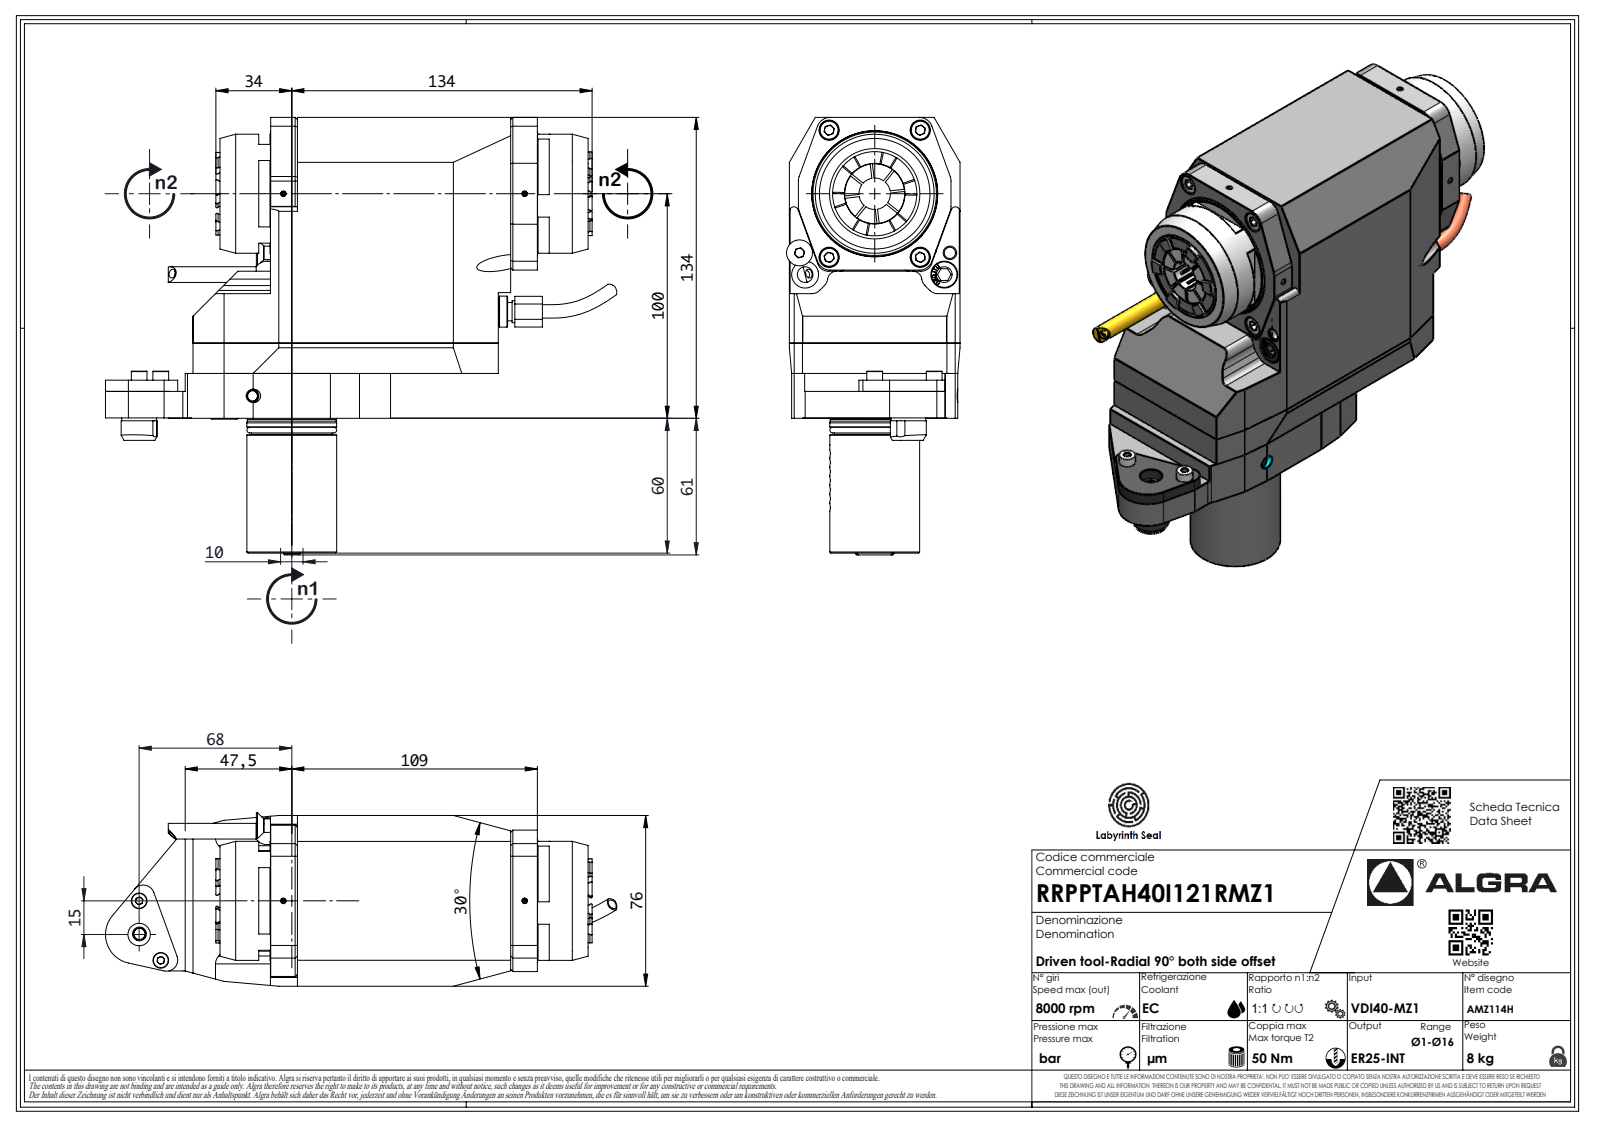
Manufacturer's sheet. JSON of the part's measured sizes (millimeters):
{"part_name": "RRPPTAH40I121RMZ1", "step_written_by": "SolidWorks 2023 (AUTOMOTIVE_DESIGN)", "units": "millimeters", "bodies": {"solids": 1, "faces": 599, "planar": 436, "cylindrical": 87, "other": 76}, "overall_size": [227.81, 194.8, 76], "volume_mm3": 1331000, "surface_area_mm2": 94605, "round_holes": [[5, 2], [2.1, 1], [4, 1], [6, 1]], "round_bosses_or_shafts": [[7, 3], [53, 1], [40, 1], [39.6, 1], [36, 1], [16, 1], [15.5, 1], [9.8, 1]], "partial_cylinders_radius": [[6, 10], [5, 8], [0.3, 7], [0.33, 7], [0.52, 7], [3.7, 7], [2, 3], [4, 2]], "face_to_face_distances": [76, 134, 20, 114, 12, 22.6, 141.4, 53.5, 88, 34.5]}
